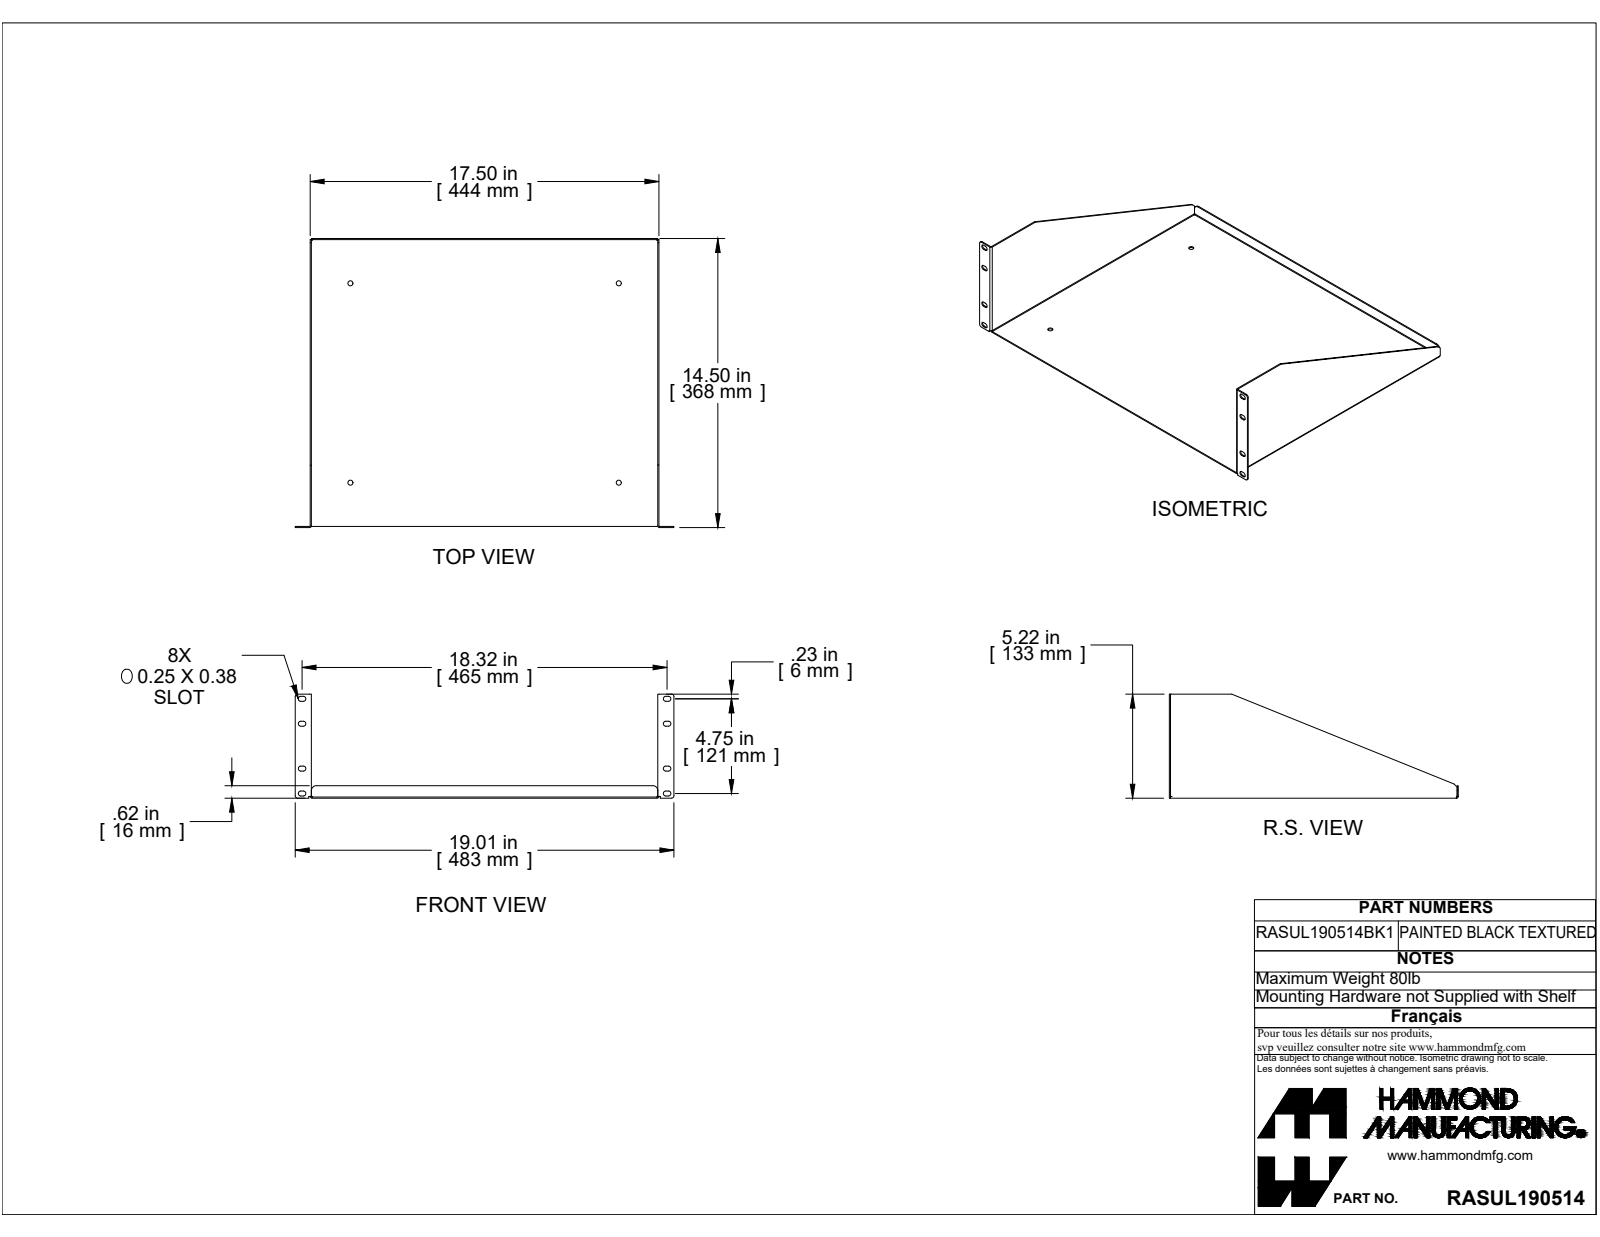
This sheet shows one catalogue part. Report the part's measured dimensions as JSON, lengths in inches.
{"part_name": "RASUL190514BK1", "step_written_by": "SolidWorks 2019 (CONFIG_CONTROL_DESIGN)", "units": "inches", "bodies": {"solids": 0, "faces": 102, "planar": 58, "cylindrical": 40, "other": 4}, "overall_size": [19.006, 14.5, 5.218], "round_bosses_or_shafts": [[0.25, 4]], "partial_cylinders_radius": [[0.125, 20], [0.029, 5], [0.086, 5], [0.055, 3], [0.25, 2]], "face_to_face_distances": [0.057, 17.443, 17.386, 17.5, 14.386, 14.443, 0.057, 14.443, 14.5, 0.625]}
